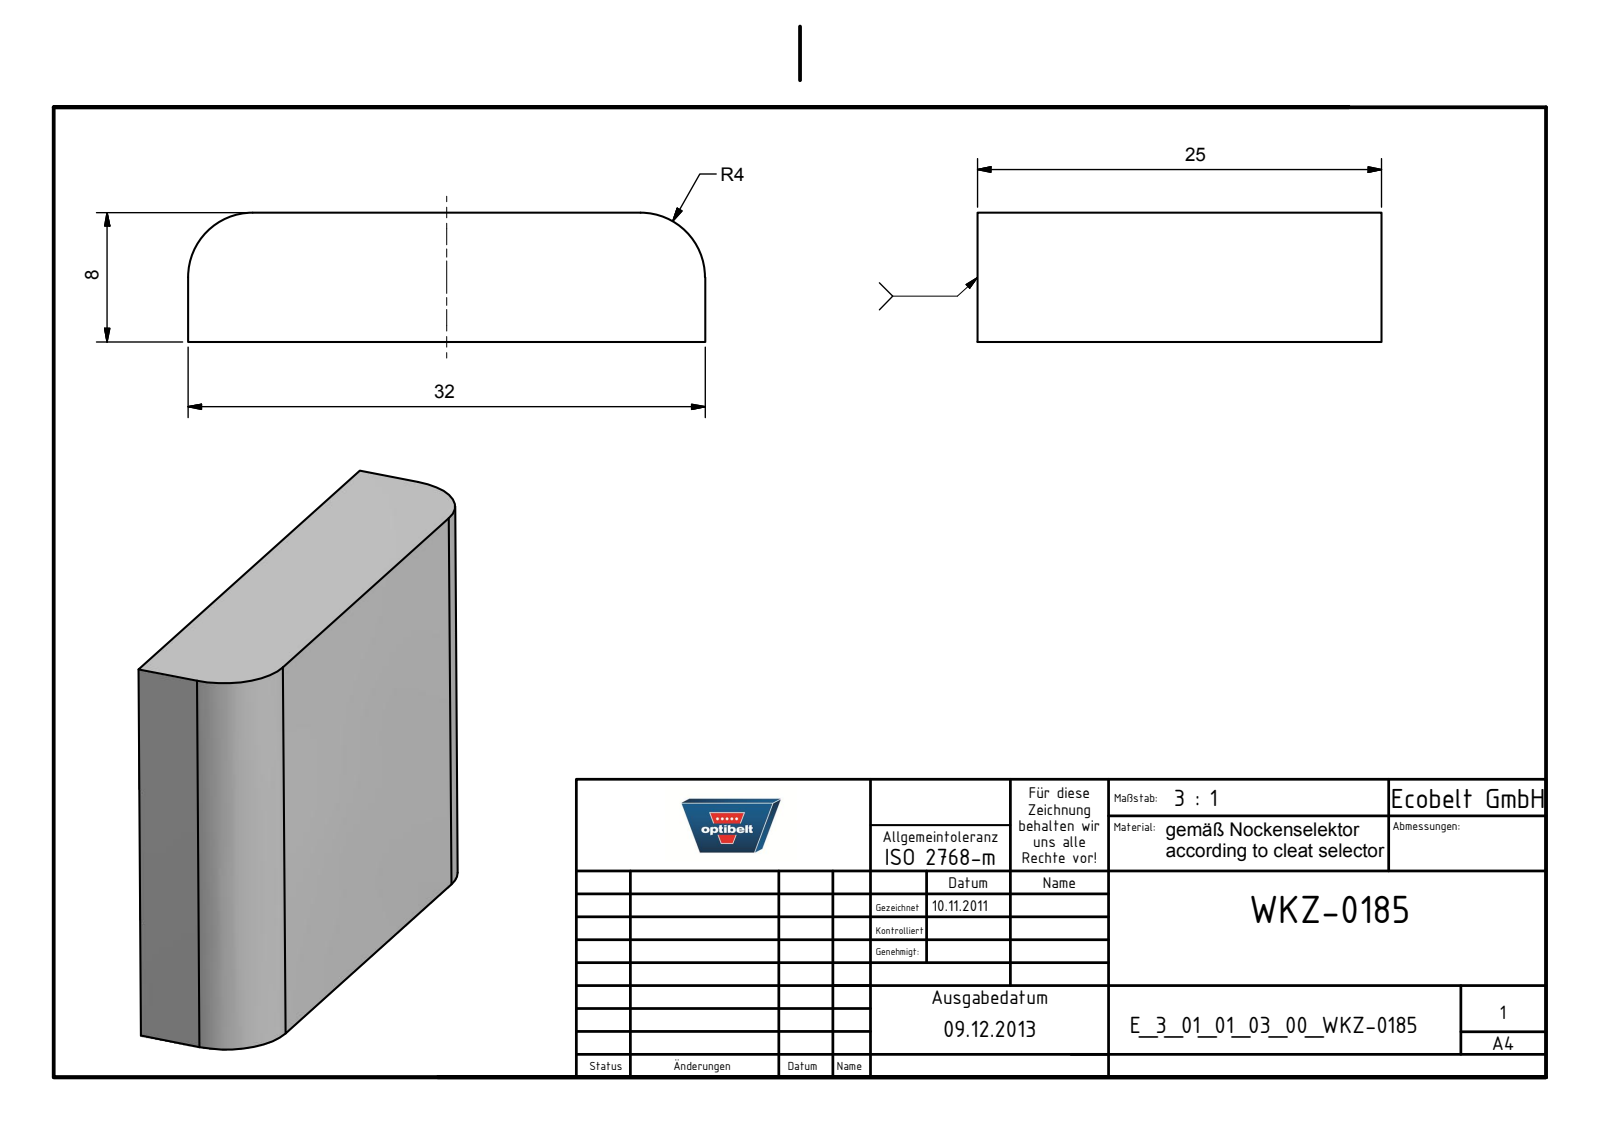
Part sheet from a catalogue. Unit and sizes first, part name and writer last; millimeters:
Units: millimetres
Overall size (bounding box): 32 × 25 × 8
Partial cylindrical surfaces — rounded edges, fillets, slot ends (radius × count): R4 ×2
Main face-to-face distances: 8, 25, 32
Volume: 6 228 mm³ · Surface area: 2 412 mm²
Bodies: 1 solid, 8 faces (6 planar, 2 cylindrical, 0 other)
Part name (STEP PRODUCT): E_3_01_01_03_00_WKZ-0185
STEP written by: Autodesk Inventor 2021 (AUTOMOTIVE_DESIGN)
